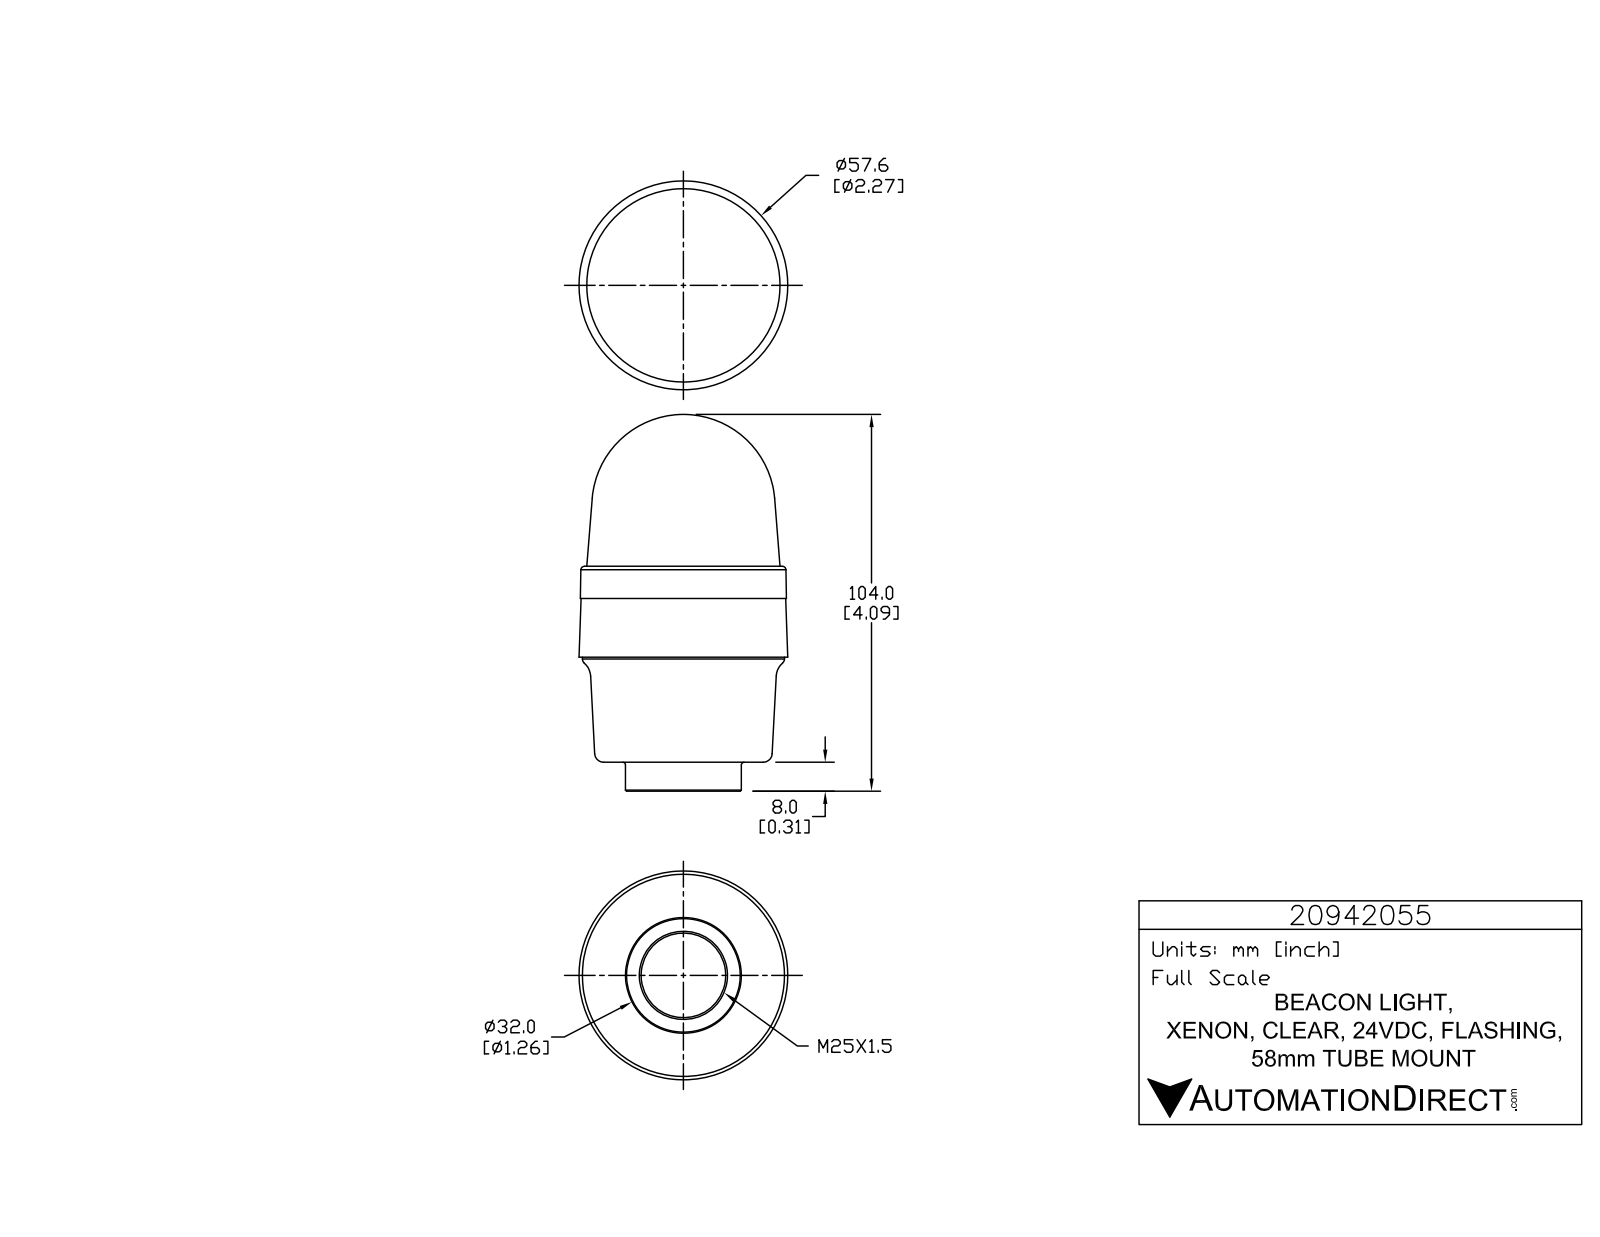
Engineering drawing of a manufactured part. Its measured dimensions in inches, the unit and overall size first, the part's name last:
Units: inches
Overall size (bounding box): 4.051 × 2.269 × 2.269
Round holes (diameter × count): ⌀0.039 ×3, ⌀0.92 ×1
Round bosses / shafts (diameter × count): ⌀0.226 ×3, ⌀0.056 ×3, ⌀2.197 ×1, ⌀1.26 ×1
Partial cylindrical surfaces — rounded edges, fillets, slot ends (radius × count): R0.008 ×6, R0.008 ×6, R0.008 ×6, R0.131 ×6, R0.004 ×3, R0.005 ×3, R0.008 ×3, R0.008 ×3
Main face-to-face distances: 0.315, 1.142, 1.457, 0.988, 2.13, 2.445, 0.35, 0.638, 1.78, 2.094
Volume: 11.72 in³ · Surface area: 29.93 in²
Bodies: 1 solid, 791 faces (525 planar, 168 cylindrical, 98 other)
Part name (STEP PRODUCT): 20942055
STEP written by: SolidWorks 2015 (AUTOMOTIVE_DESIGN)
